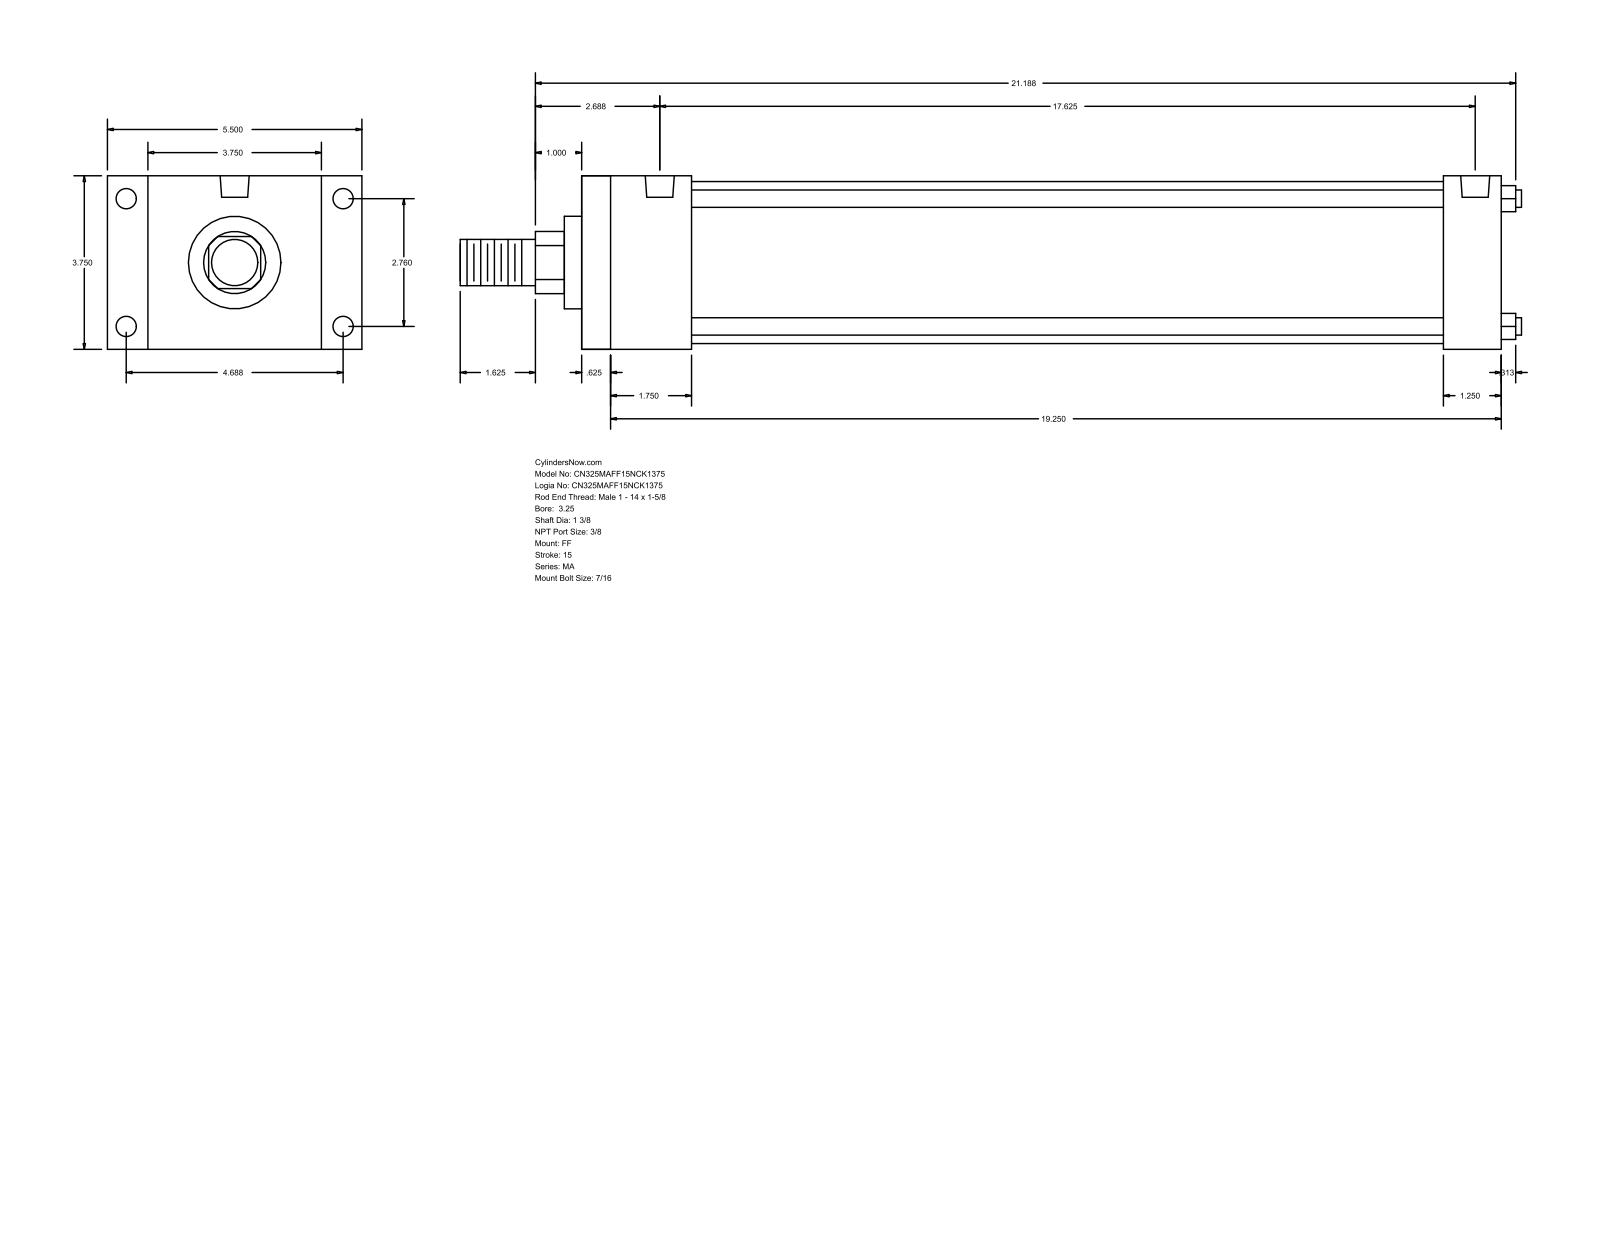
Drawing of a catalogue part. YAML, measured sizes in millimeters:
part_name: "MA_FF__0325_1.375"
step_written_by: "GSSL Pune (CONFIG_CONTROL_DESIGN)"
units: millimeters
bodies: {solids: 0, faces: 92, planar: 64, cylindrical: 28, other: 0}
overall_size: [582.61, 139.7, 95.25]
round_holes:
  - {diameter: 11.11, count: 8}
  - {diameter: 15.93, count: 2}
round_bosses_or_shafts:
  - {diameter: 9.53, count: 4}
  - {diameter: 88.9, count: 1}
  - {diameter: 50.8, count: 1}
  - {diameter: 34.92, count: 1}
  - {diameter: 25.4, count: 1}
partial_cylinders:
  - {radius: 17.06, count: 1}
face_to_face_distances: [95.24, 504.83, 15.87, 488.96, 22.23, 117.47, 60.32, 473.08, 44.45, 457.21]
hole_center_spacings: [70.1, 119.06, 138.16, 438.15, 4.76, 4.77, 442.91, 442.92]
